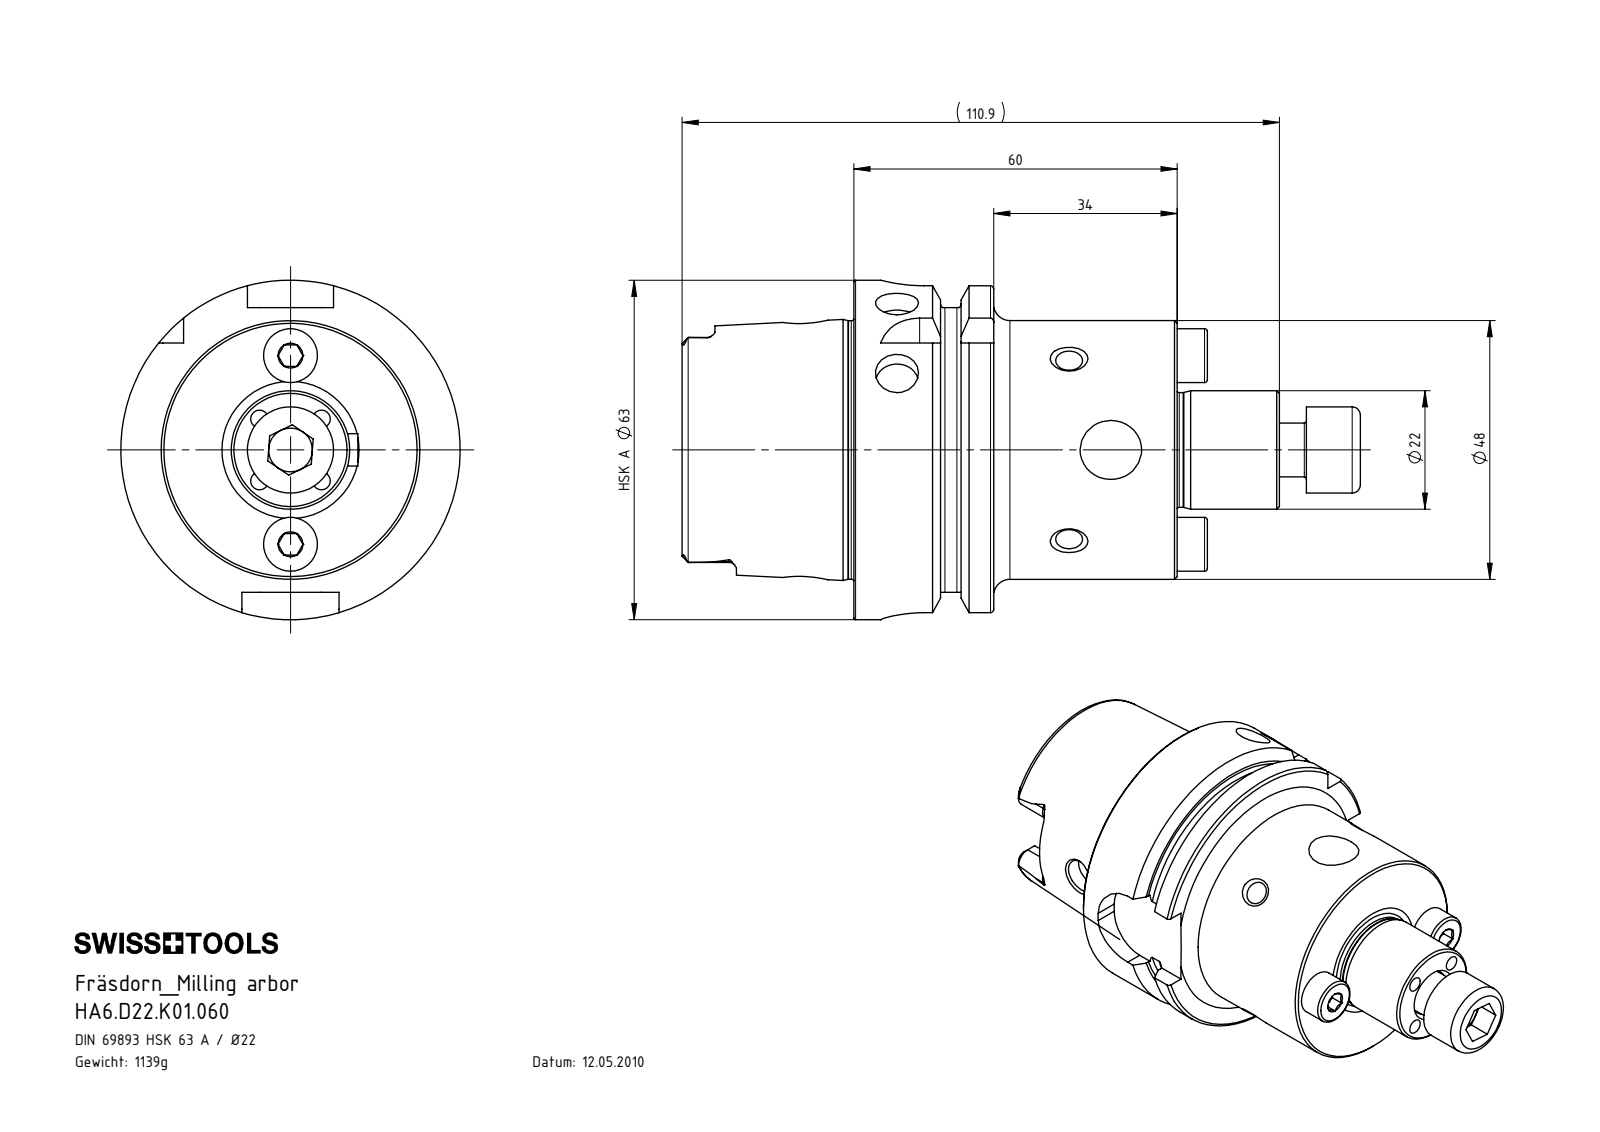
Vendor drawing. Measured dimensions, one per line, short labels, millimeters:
name: HA6.D22.K01.060; DIN 6885 - 6x6x14; HA6-D22.K01.060_D_Fertigbearbeitung; ISO 4762 - M10 x 25 (+1 more)
written by: SolidWorks 2017 (AUTOMOTIVE_DESIGN)
unit: mm
bodies: 5 solids, 390 faces (96 planar, 116 cylindrical, 178 other)
size: 125.9 × 63 × 63
volume: 148 289 mm³; area: 36 520 mm²
holes: 6× ⌀3.3, 4× ⌀5, 4× ⌀8, 2× ⌀4.2, 1× ⌀7.5, 1× ⌀8.5, 1× ⌀10, 1× ⌀10.5, 1× ⌀17, 1× ⌀19, 1× ⌀34, 1× ⌀40
bosses: 3× ⌀10, 2× ⌀5, 2× ⌀3.8, 1× ⌀63, 1× ⌀54.95, 1× ⌀48, 1× ⌀47.94, 1× ⌀22
rounds: 6× R1.4, 4× R2.88, 4× R3, 4× R8
face distances: 60, 25.95, 34.05, 16, 50.05, 9.95, 31.9, 41.85, 57.85, 91.9
hole spacings: 8.13, 11.05, 11.5, 13.08, 23.95, 16.26, 17.5, 35
